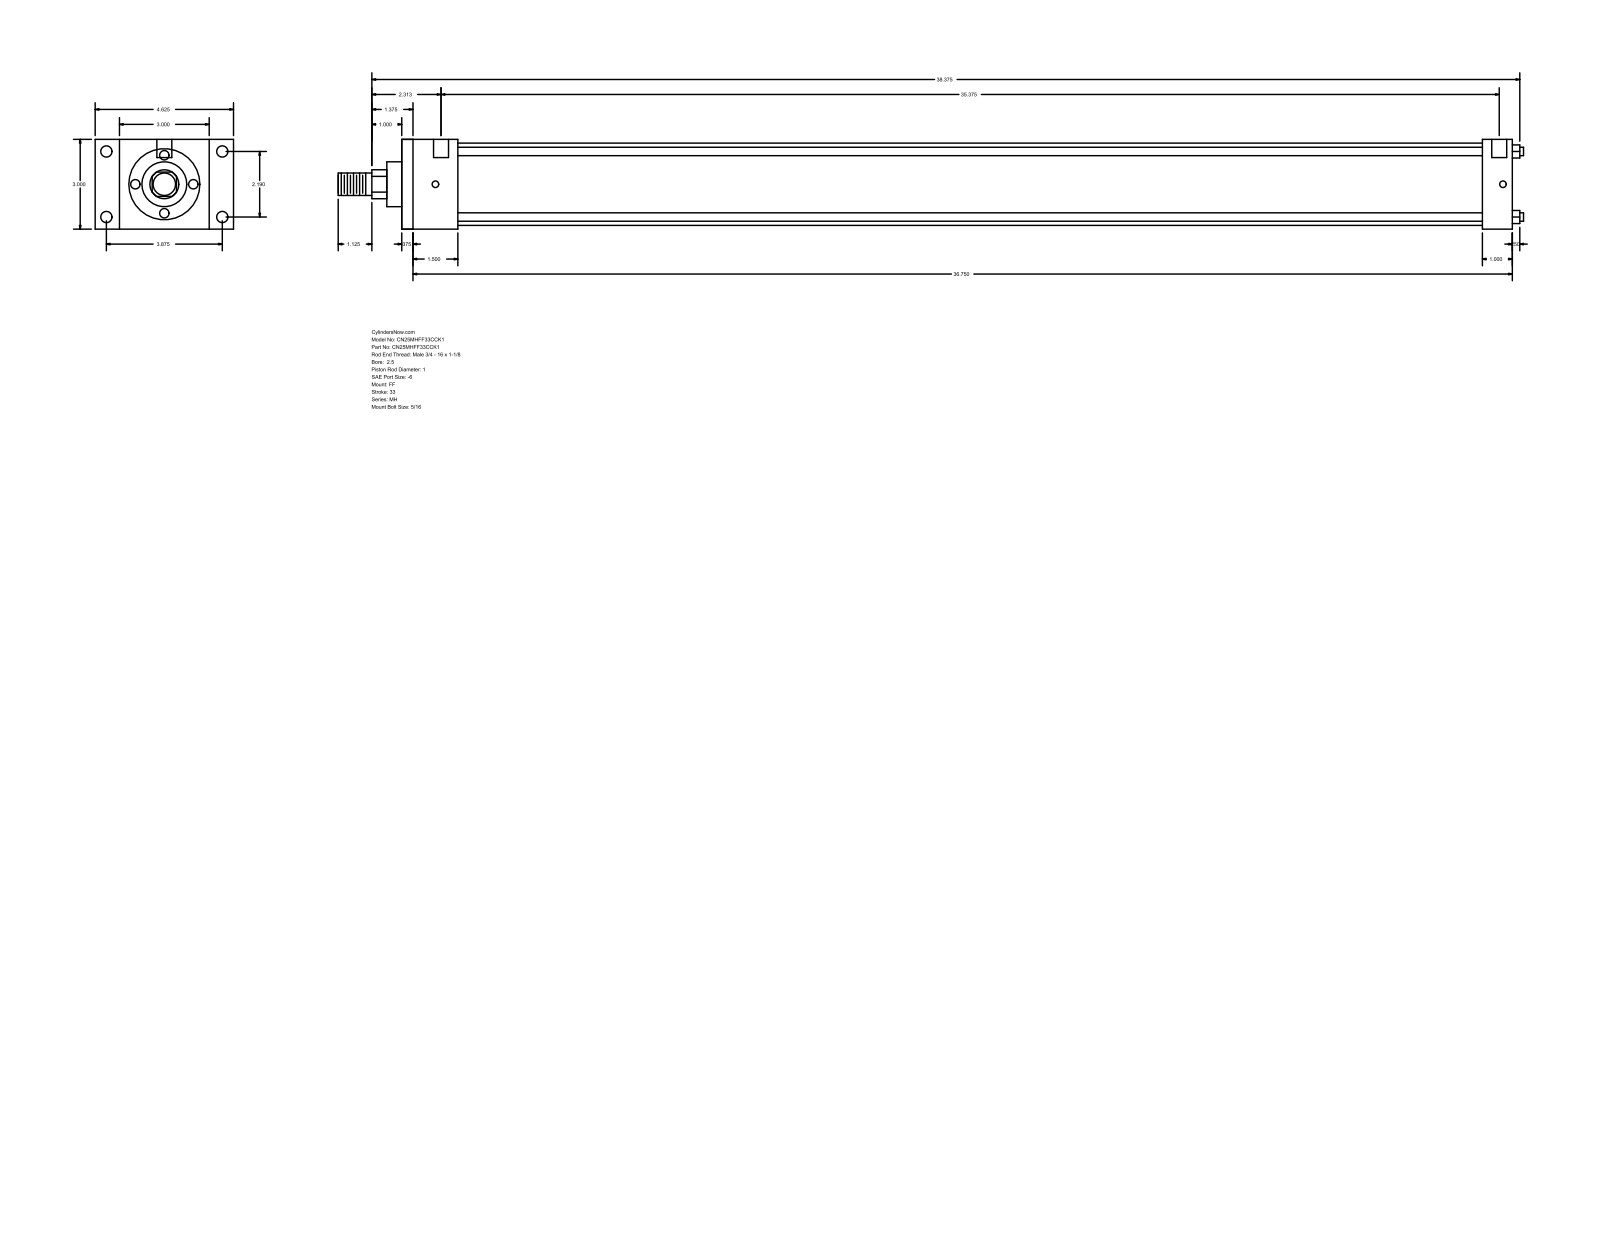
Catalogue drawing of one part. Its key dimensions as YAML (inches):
part_name: "MH_FF__0250_1"
step_written_by: "GSSL Pune (CONFIG_CONTROL_DESIGN)"
units: inches
bodies: {solids: 0, faces: 92, planar: 64, cylindrical: 28, other: 0}
overall_size: [39.625, 4.625, 3]
round_holes:
  - {diameter: 0.219, count: 4}
  - {diameter: 0.375, count: 4}
  - {diameter: 0.5, count: 2}
round_bosses_or_shafts:
  - {diameter: 0.281, count: 4}
  - {diameter: 2.75, count: 1}
  - {diameter: 1.5, count: 1}
  - {diameter: 1, count: 1}
  - {diameter: 0.75, count: 1}
partial_cylinders:
  - {radius: 0.484, count: 1}
face_to_face_distances: [3, 37.125, 0.375, 36.75, 1, 1.875, 36.125, 1.5, 35.75, 34.25]
hole_center_spacings: [2.19, 3.875, 4.451, 35.687, 0.125, 0.187, 35.375, 35.5]
